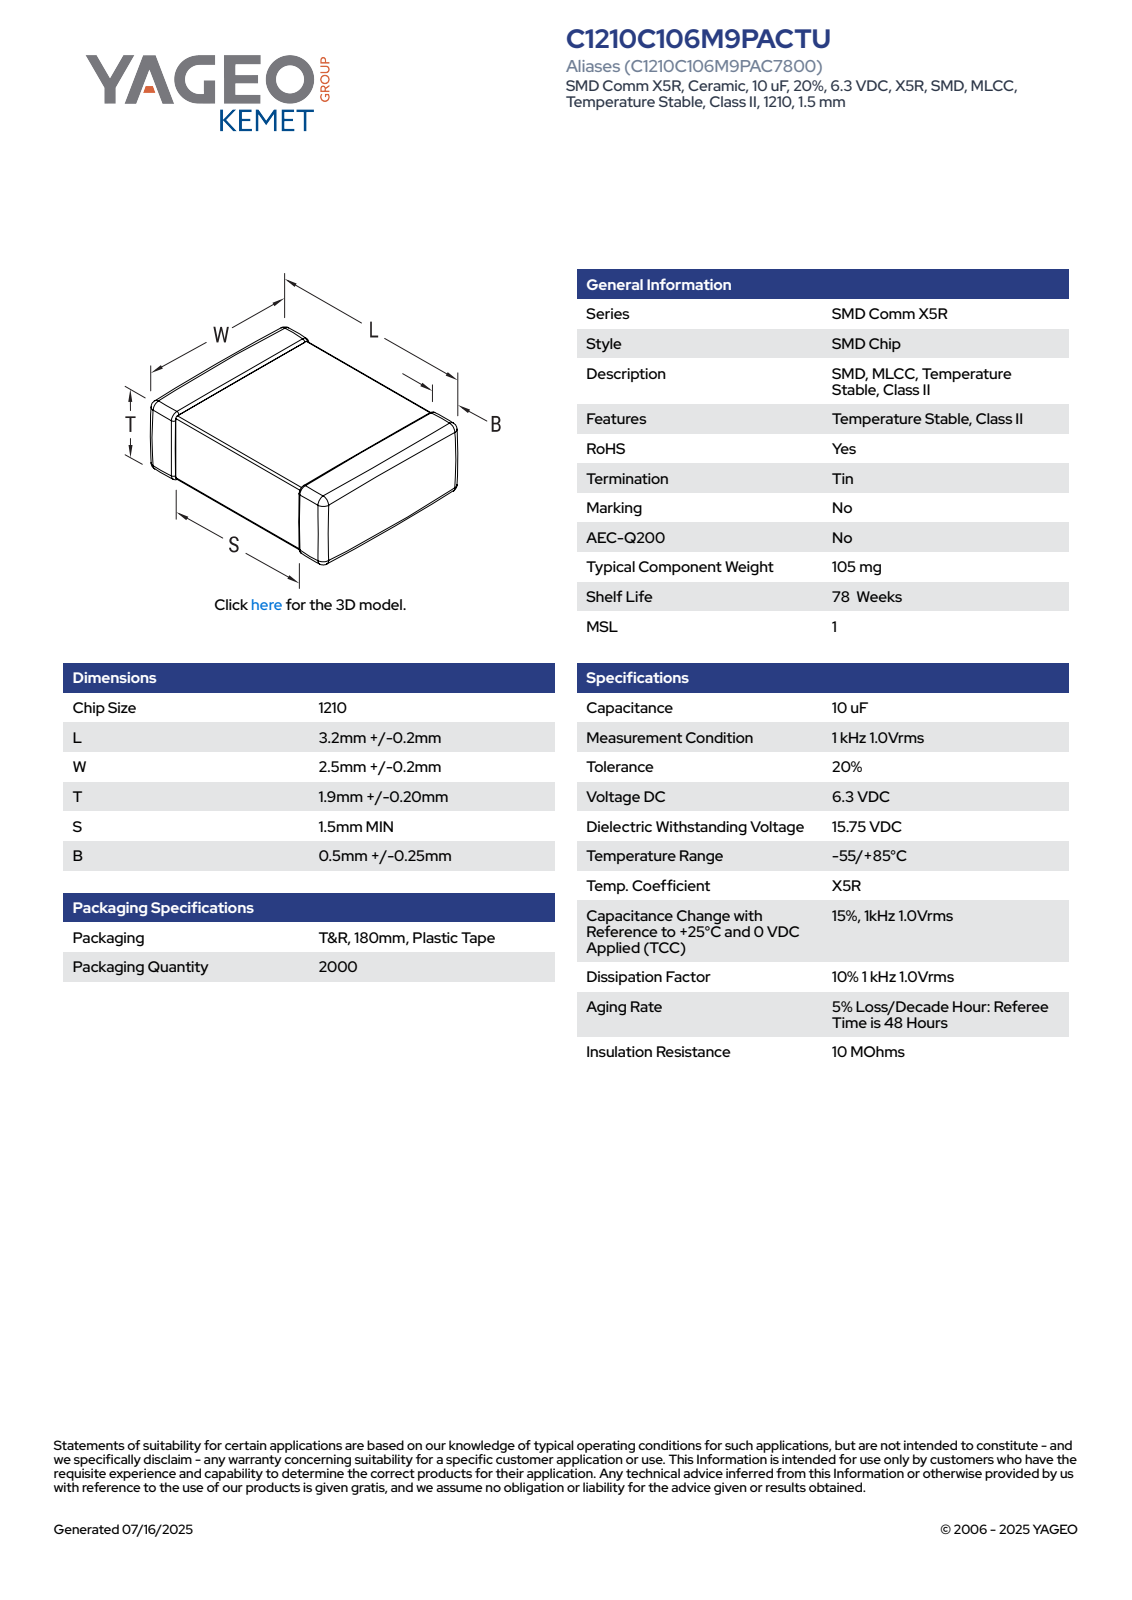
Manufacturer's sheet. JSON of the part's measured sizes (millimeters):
{"part_name": "CCS_CCSTD_1210_L3.4W2.7T2.1B0.5", "step_written_by": "SolidWorks 2021 (AUTOMOTIVE_DESIGN)", "units": "millimeters", "bodies": {"solids": 4, "faces": 125, "planar": 71, "cylindrical": 38, "other": 16}, "overall_size": [3.4, 2.7, 2.1], "volume_mm3": 18, "surface_area_mm2": 44, "face_to_face_distances": [2.04, 3.4, 2.64, 1.98, 2.58, 2.1, 2.7, 2.05, 1.99, 0.4]}
